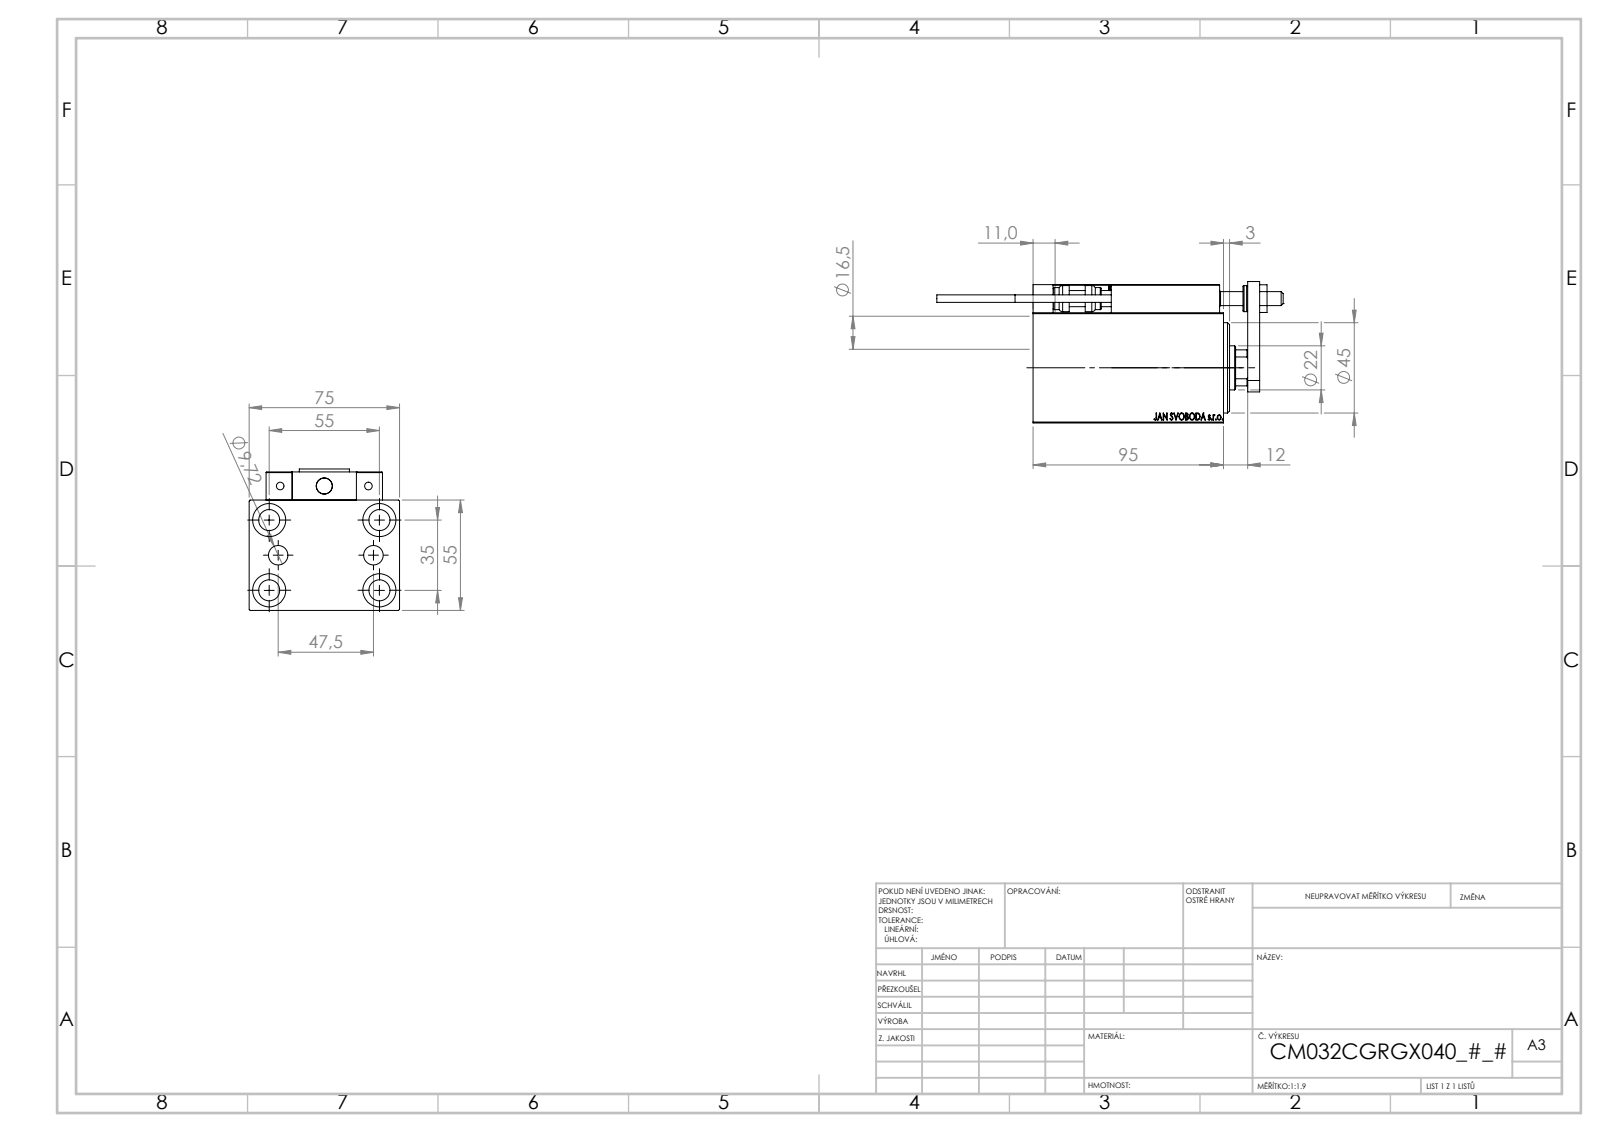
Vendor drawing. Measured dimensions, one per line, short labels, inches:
name: ALLEN BOLT D8; V450CM_C_Body; MAGNET; V450CM_VC_B (+7 more)
written by: SolidWorks 2019 (CONFIG_CONTROL_DESIGN)
unit: in
bodies: 23 solids, 1278 faces (560 planar, 184 cylindrical, 534 other)
size: 6.799 × 2.953 × 2.776
volume: 23.29 in³; area: 144.2 in²
holes: 6× ⌀0.157, 5× ⌀0.315, 5× ⌀0.413, 5× ⌀0.65, 4× ⌀0.126, 2× ⌀0.197, 2× ⌀0.383, 1× ⌀0.276, 1× ⌀0.866, 1× ⌀1.004, 1× ⌀1.26, 1× ⌀1.339
bosses: 2× ⌀0.197, 2× ⌀0.15, 1× ⌀0.512, 1× ⌀0.433
rounds: 30× R0.012, 2× R0.118, 1× R0.413
face distances: 2.165, 2.953, 0.551, 0.197, 2.717, 1.772, 0.394, 0.472, 0.236, 0.984
hole spacings: 0.705, 1.283, 2.132, 0.448, 0.787, 0.935, 1.165, 1.169
